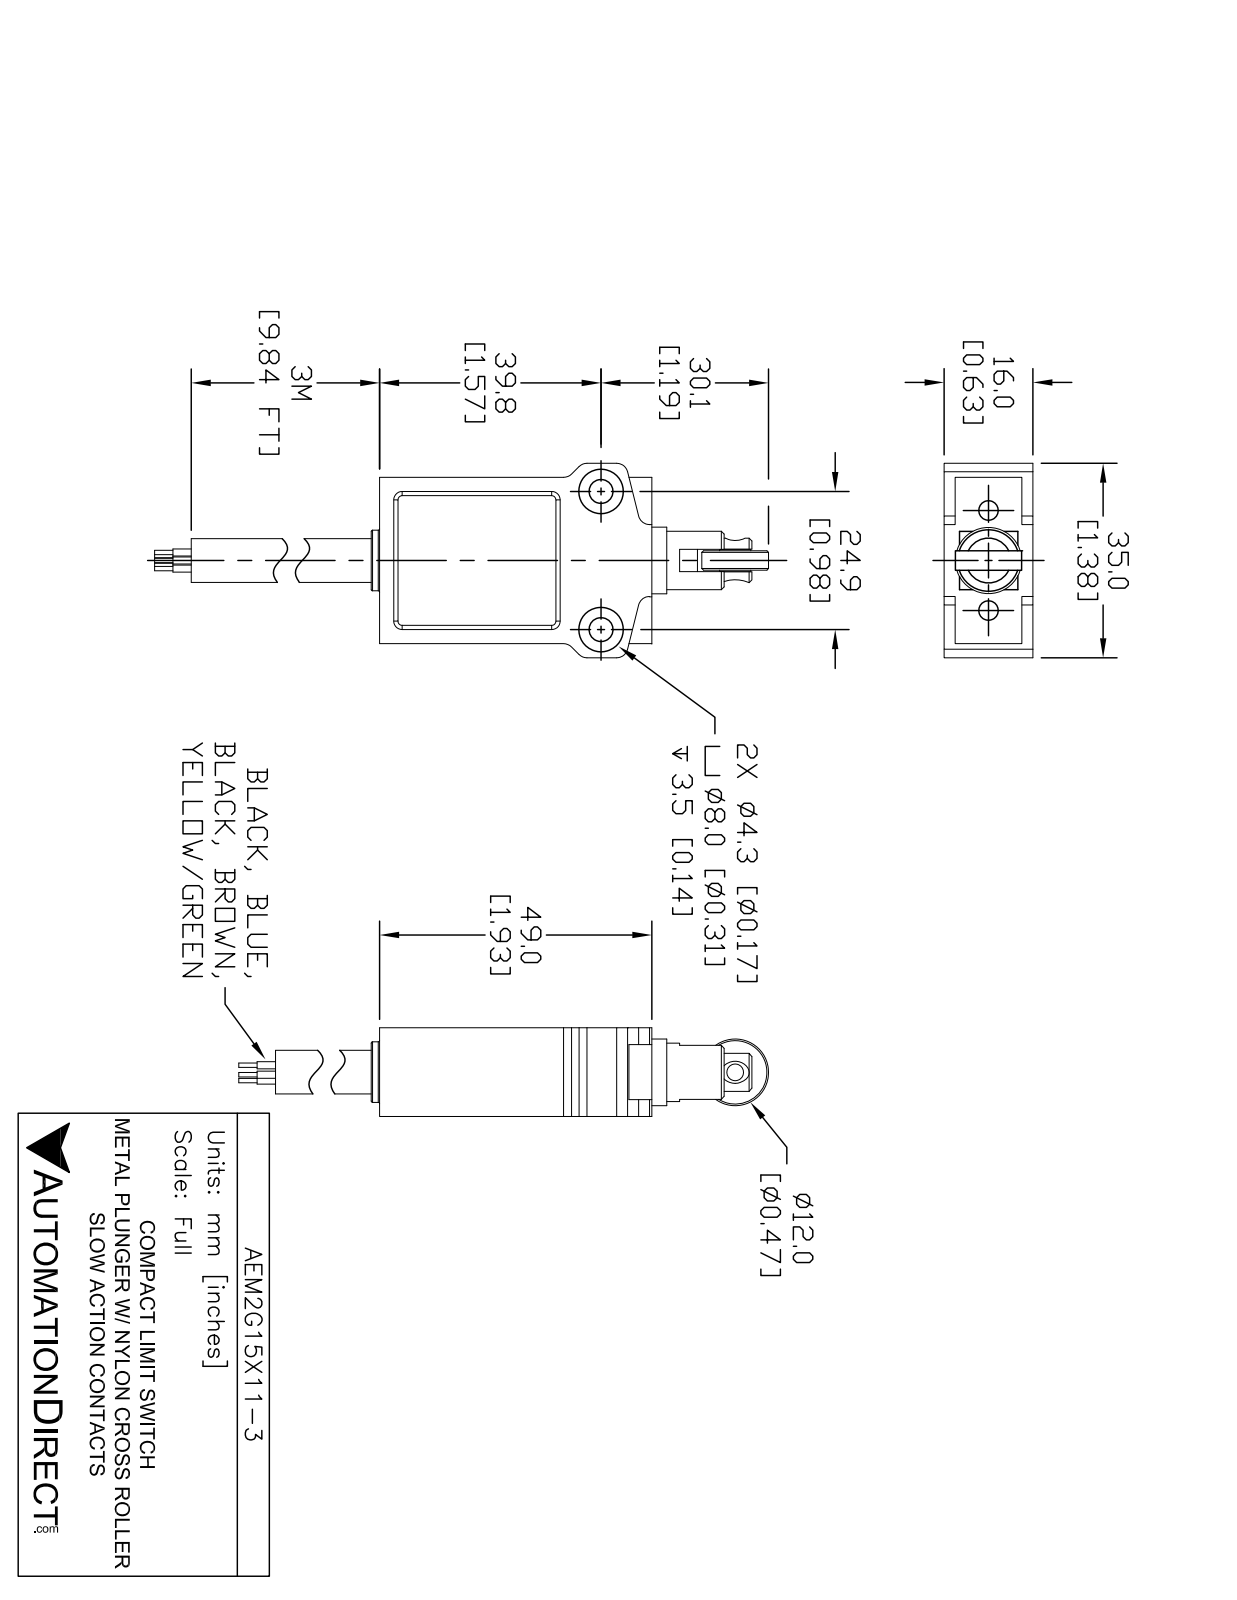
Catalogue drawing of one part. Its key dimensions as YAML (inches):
part_name: "AEM2G15X11-3_Default"
step_written_by: "SolidWorks 2021 (CONFIG_CONTROL_DESIGN)"
units: inches
bodies: {solids: 2, faces: 115, planar: 54, cylindrical: 41, other: 20}
overall_size: [3.385, 1.38, 0.63]
volume: 1.43
surface_area: 11.87
round_holes:
  - {diameter: 0.177, count: 2}
  - {diameter: 0.344, count: 2}
round_bosses_or_shafts:
  - {diameter: 0.05, count: 5}
  - {diameter: 0.031, count: 5}
  - {diameter: 0.47, count: 2}
  - {diameter: 0.43, count: 1}
  - {diameter: 0.41, count: 1}
  - {diameter: 0.31, count: 1}
partial_cylinders:
  - {radius: 0.03, count: 8}
  - {radius: 0.08, count: 8}
  - {radius: 0.135, count: 1}
face_to_face_distances: [0.03, 0.6, 0.57, 0.63, 1.18, 1.93, 0.51, 0.67, 0.505, 0.675]
hole_center_spacings: [0.98]
